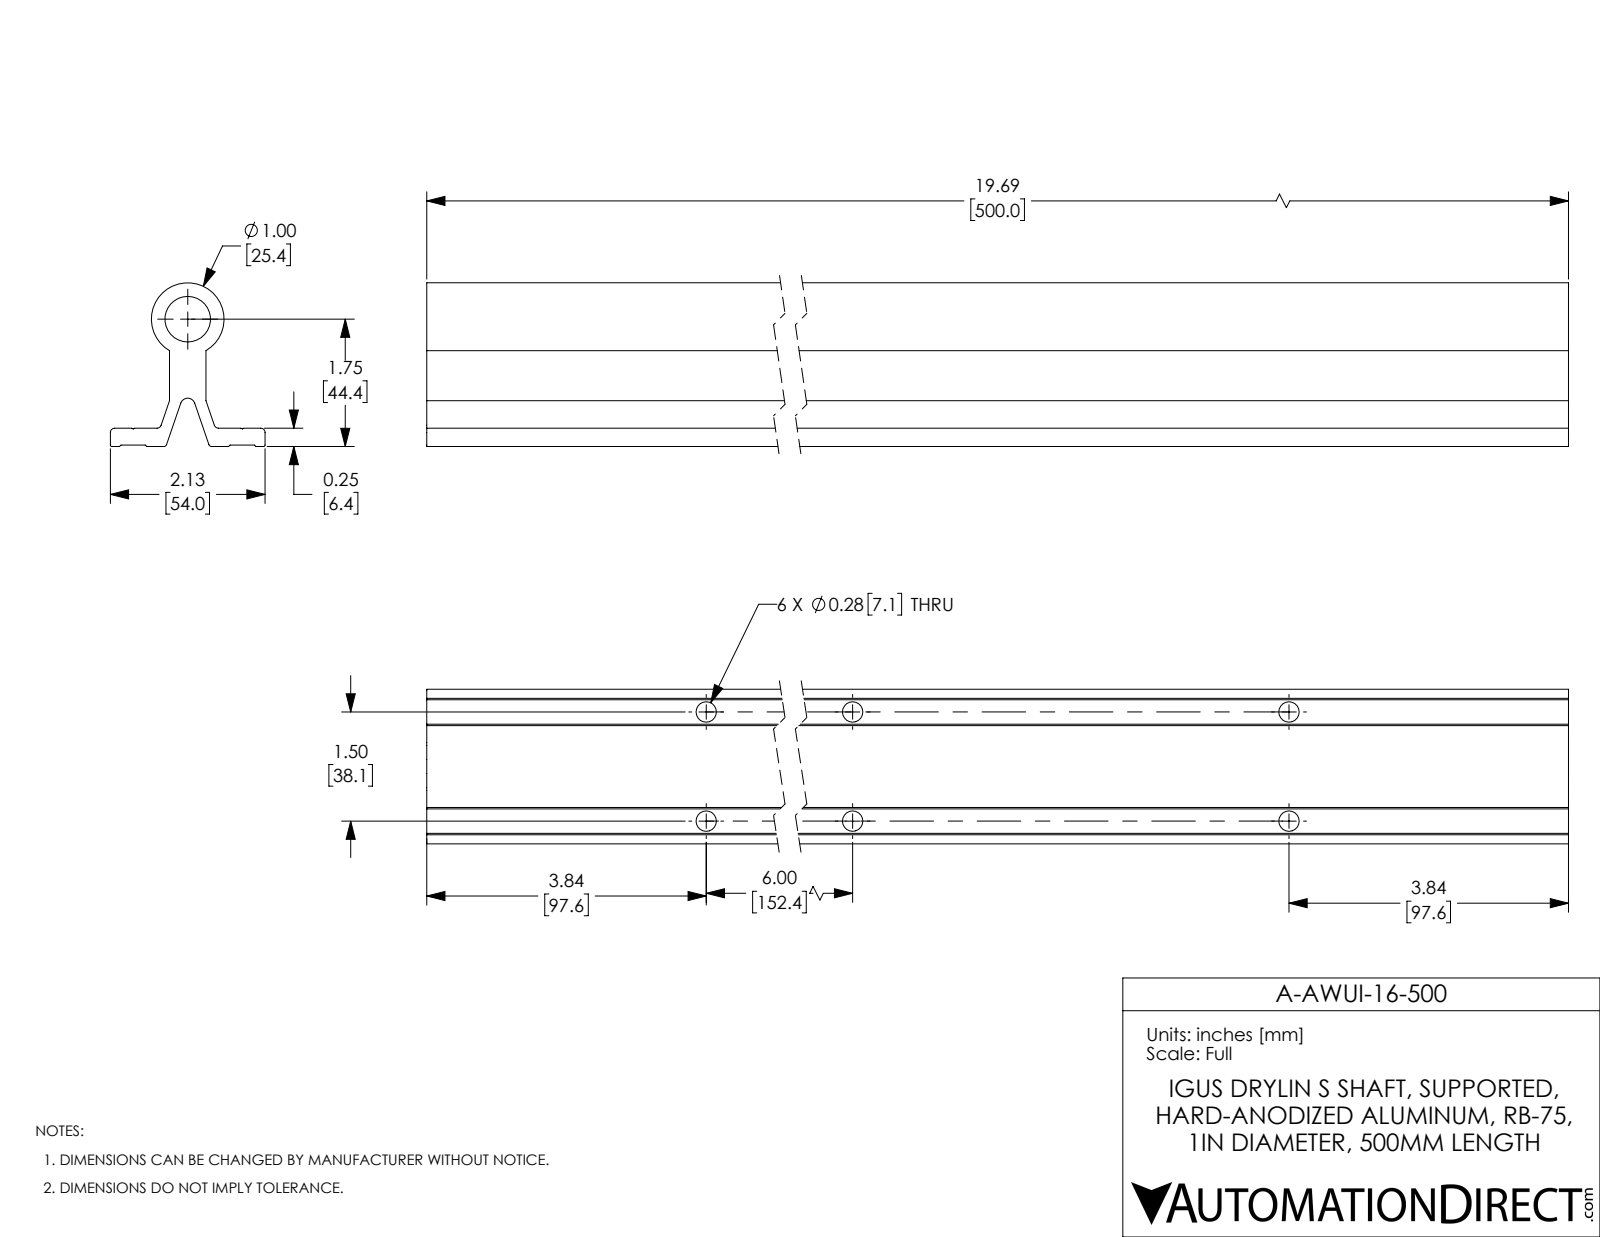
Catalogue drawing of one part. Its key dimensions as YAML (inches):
part_name: "A-AWUI-16-500"
step_written_by: "SolidWorks 2017 (AUTOMOTIVE_DESIGN)"
units: inches
bodies: {solids: 1, faces: 64, planar: 40, cylindrical: 24, other: 0}
overall_size: [19.685, 2.25, 2.126]
volume: 25.73
surface_area: 231.5
round_holes:
  - {diameter: 0.28, count: 6}
  - {diameter: 0.626, count: 1}
round_bosses_or_shafts:
  - {diameter: 1, count: 1}
partial_cylinders:
  - {radius: 0.059, count: 4}
  - {radius: 0.02, count: 2}
  - {radius: 0.039, count: 2}
  - {radius: 0.1, count: 1}
face_to_face_distances: [0.157, 0.252, 0.02, 0.232, 0.813, 2.126, 1.313, 19.685, 1.061, 0.75]
hole_center_spacings: [6, 6.185, 1.5, 12, 12.093]
